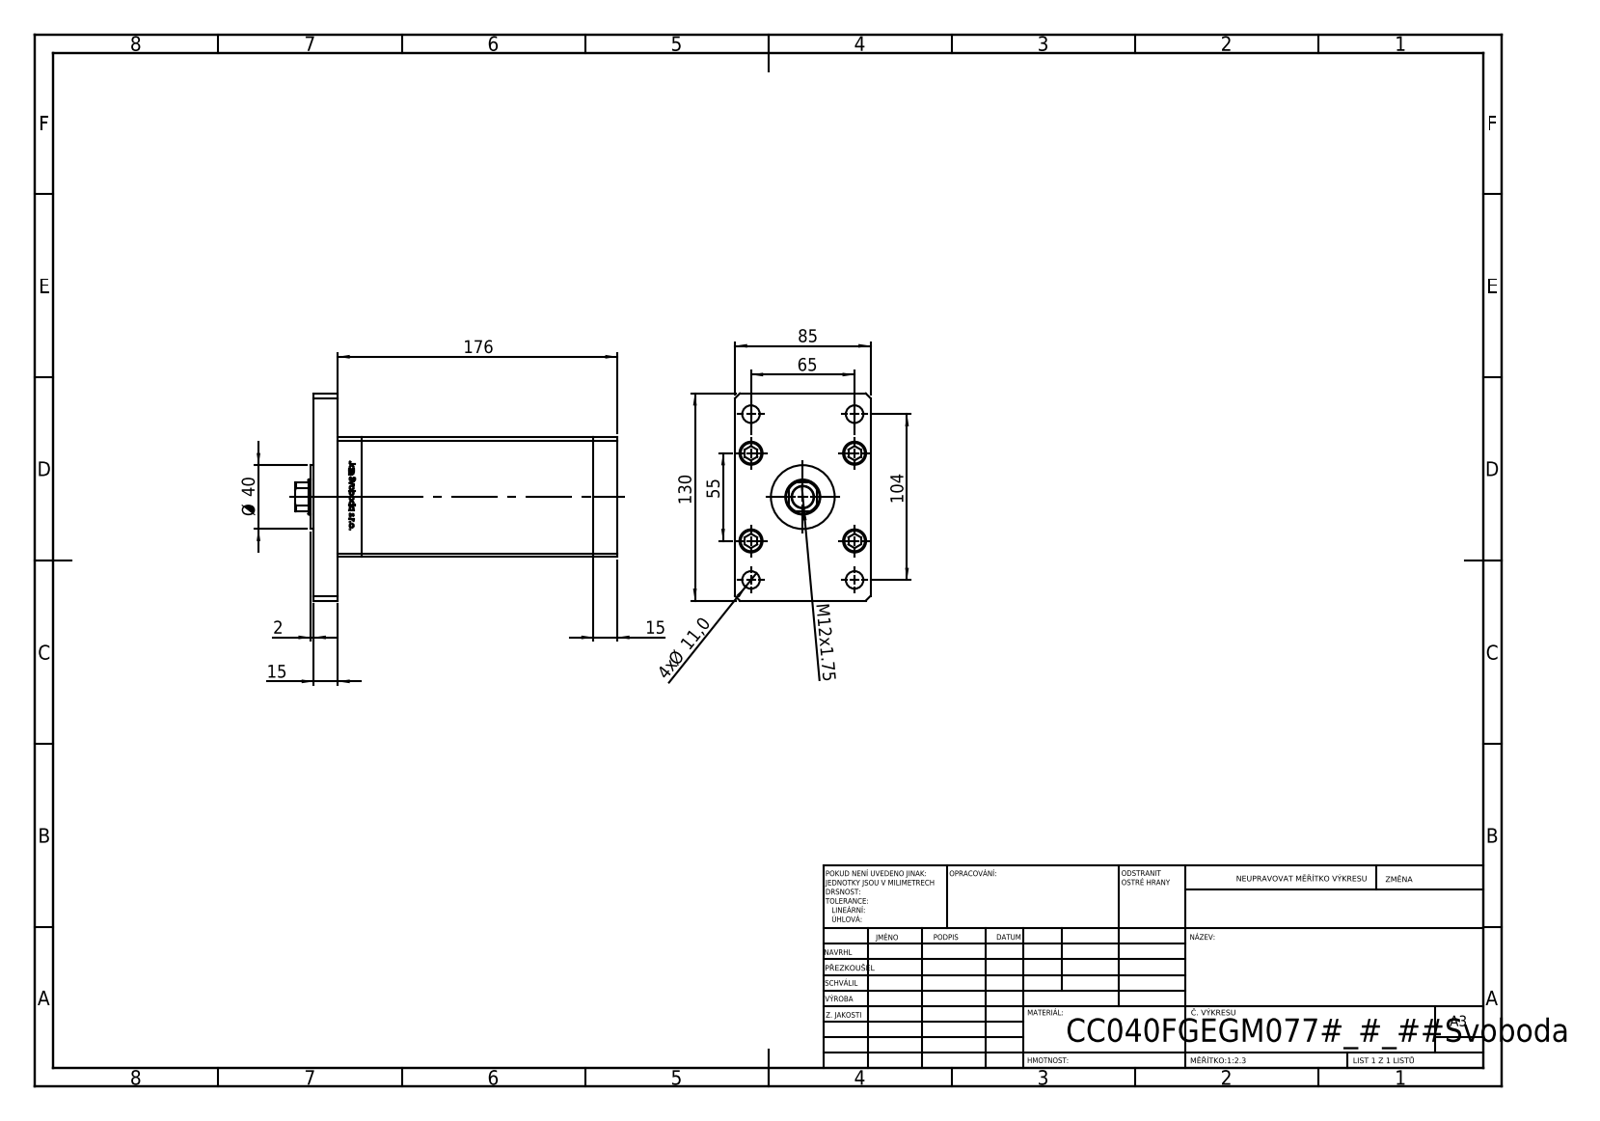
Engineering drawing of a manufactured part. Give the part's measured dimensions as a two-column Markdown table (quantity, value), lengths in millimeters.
| quantity | value |
| --- | --- |
| part name | V220C_VC_F; V220C_F; V220C_FRONT_F; V220C BACK_F (+2 more) |
| STEP written by | SolidWorks 2019 (CONFIG_CONTROL_DESIGN) |
| units | millimeters |
| bodies | 19 solids, 1310 faces (517 planar, 187 cylindrical, 606 other) |
| overall size | 202 × 130 × 85 |
| volume | 1 149 000 mm³ |
| surface area | 197 285 mm² |
| round holes (diameter × count) | 11 × 9, 15.5 × 5, 10 × 4, 14.5 × 4, 2 × 2, 13.16 × 2, 13.5 × 1, 22 × 1, 23.5 × 1 |
| round bosses / shafts (diameter × count) | 8 × 9, 14.5 × 5, 40 × 1 |
| partial cylindrical surfaces (radius × count) | 0.93 × 2, 10.5 × 1 |
| main face-to-face distances | 15, 85, 160.5, 175.5, 75, 30, 145.5, 190.5, 10.5, 27.5 |
| hole center spacings | 28, 24.5, 42.57, 61.32, 65, 69.46, 79.5, 102.69 |
